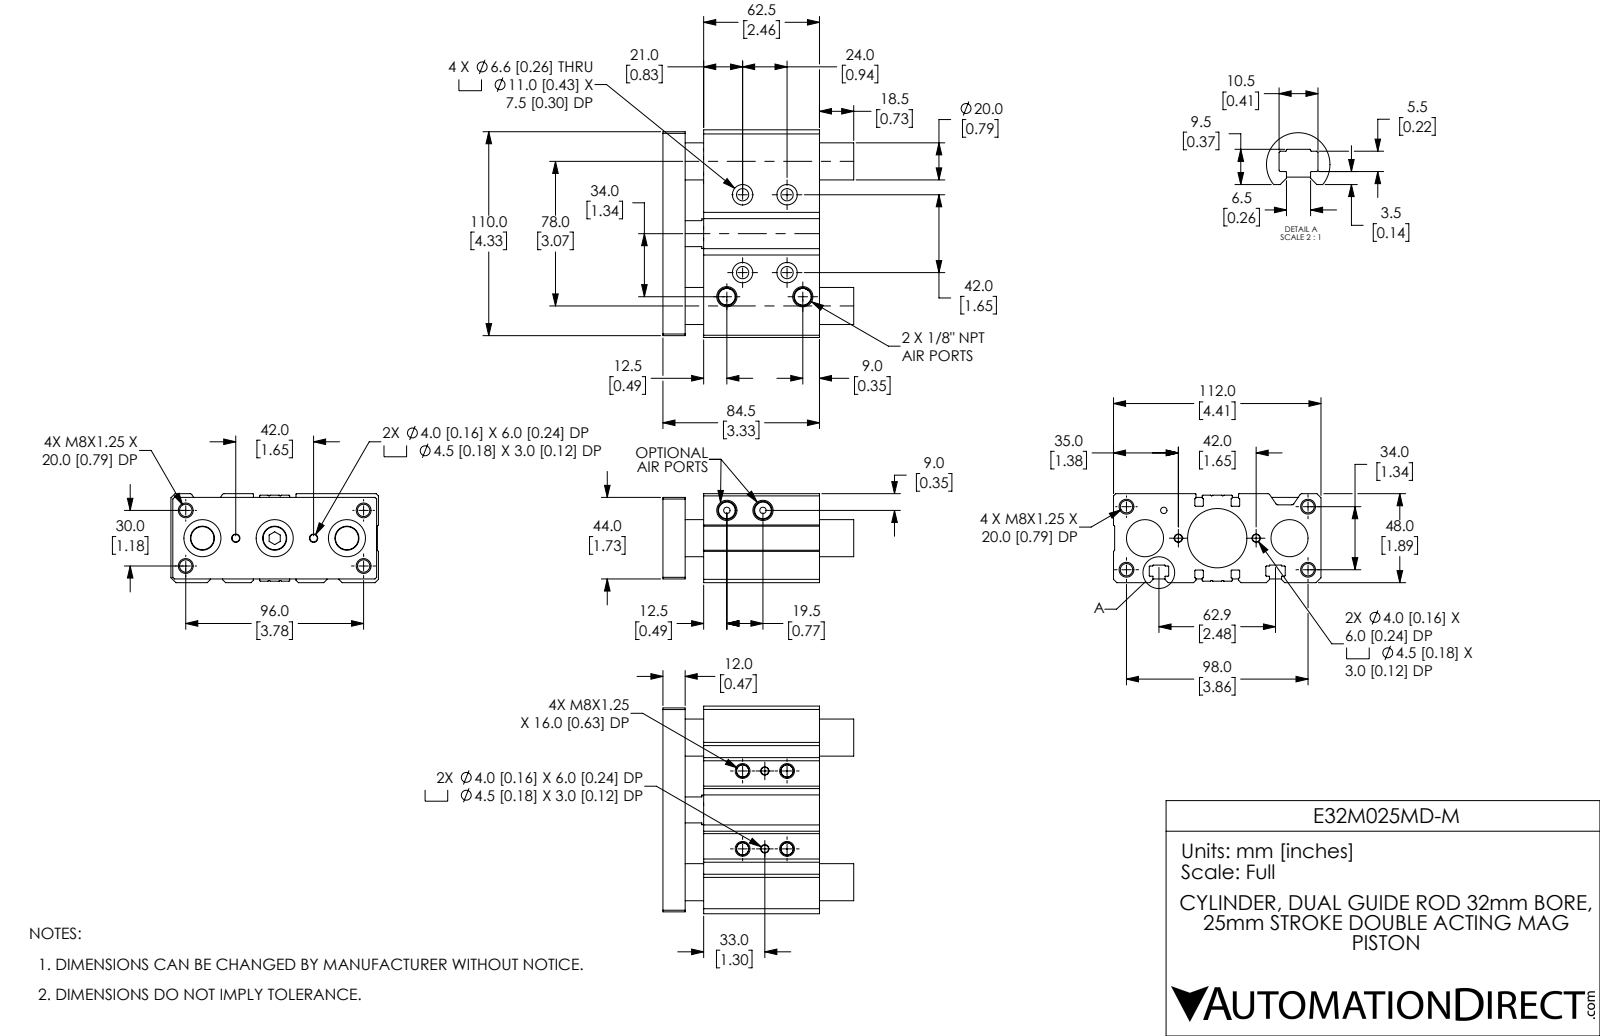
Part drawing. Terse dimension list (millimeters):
name: E32M025MD-M_ENDPLATE; E32M025MD-M; E32M025MD-M_BODY
written by: SolidWorks 2019 (CONFIG_CONTROL_DESIGN)
unit: mm
bodies: 5 solids, 423 faces (139 planar, 190 cylindrical, 94 other)
size: 112 × 103 × 48
volume: 352 235 mm³; area: 94 184 mm²
holes: 12× ⌀6.65, 4× ⌀4, 4× ⌀4.5, 4× ⌀6.6, 4× ⌀11, 3× ⌀3.43, 3× ⌀10, 3× ⌀20, 2× ⌀12.95, 1× ⌀20, 1× ⌀32, 1× ⌀32
bosses: 1× ⌀16, 1× ⌀12.95
rounds: 32× R0.2, 28× R0.4, 4× R1.2, 2× R0.3
face distances: 62.5, 22, 12, 10, 48, 84.5, 72.5, 2, 6, 46
hole spacings: 2.24, 12, 17.49, 19.72, 30.89, 32.02, 32.76, 42
